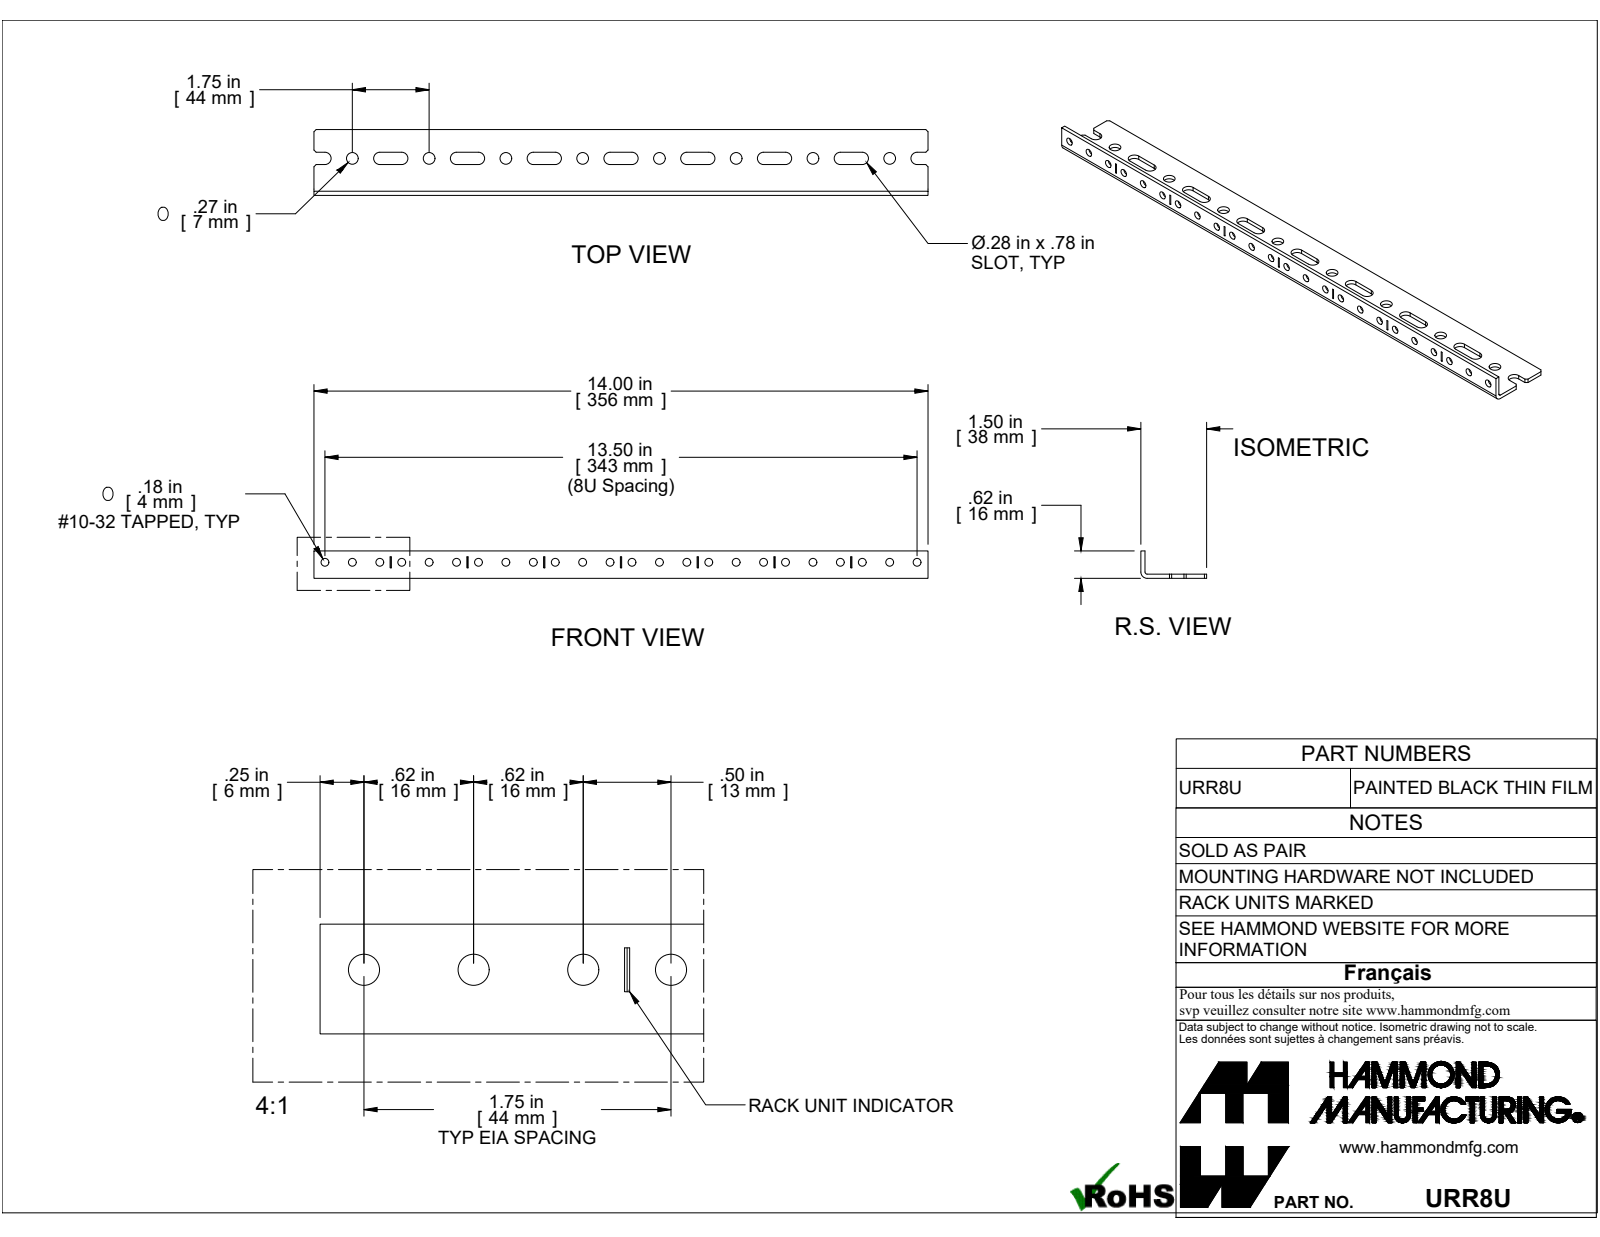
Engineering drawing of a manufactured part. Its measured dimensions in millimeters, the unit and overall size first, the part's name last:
Units: millimetres
Overall size (bounding box): 355.6 × 38.1 × 15.88
Round holes (diameter × count): ⌀4.5 ×24, ⌀6.76 ×8
Partial cylindrical surfaces — rounded edges, fillets, slot ends (radius × count): R3.57 ×16, R1.22 ×1, R3.63 ×1
Main face-to-face distances: 2.41, 15.88, 13.47, 38.1, 35.69, 17.84, 24.98, 15.43, 22.57, 7.14
Hole centre spacings: 44.45, 88.9, 133.35, 177.8, 15.87, 15.88, 28.57, 31.75
Volume: 39 194 mm³ · Surface area: 36 596 mm²
Bodies: 1 solid, 112 faces (62 planar, 50 cylindrical, 0 other)
Part name (STEP PRODUCT): COM57213-8
STEP written by: ST-DEVELOPER v16.7 (AUTOMOTIVE_DESIGN)
